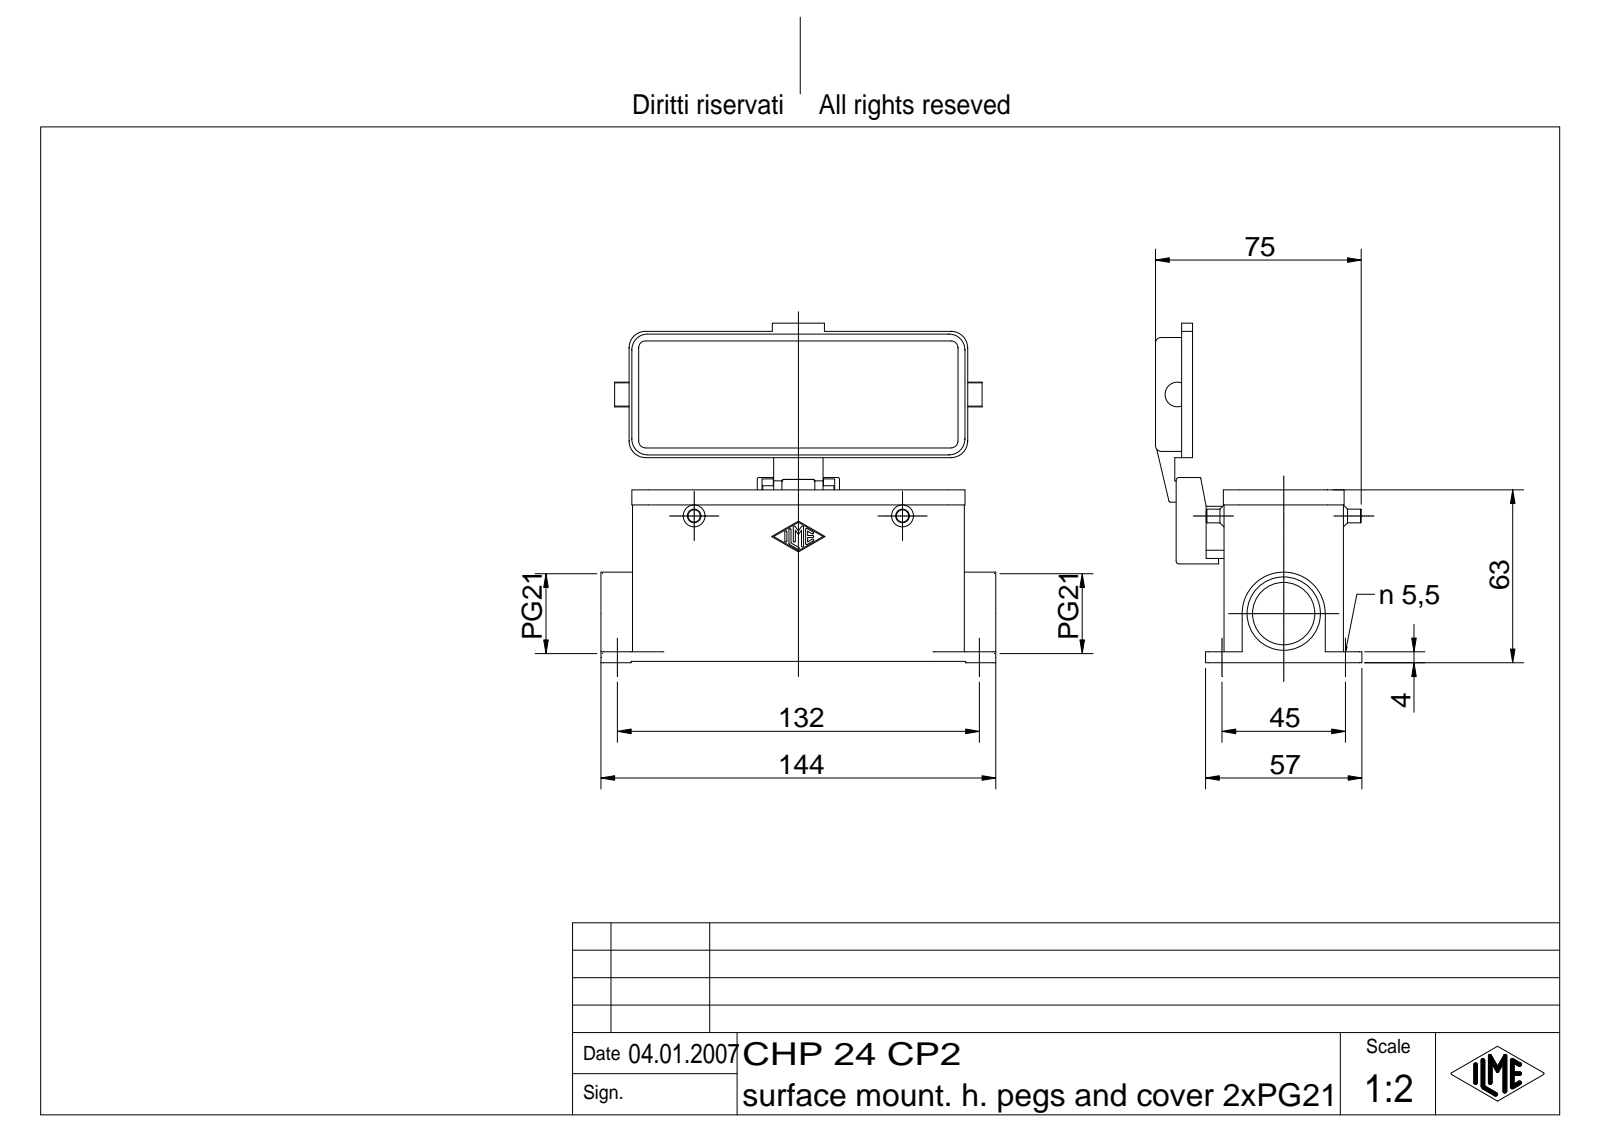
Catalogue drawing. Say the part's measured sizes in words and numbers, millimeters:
The part is named "CHP 24 CP2". Its 3-D file was written by "Autodesk Inventor 7 (AUTOMOTIVE_DESIGN)". It is 1 solid with 469 faces: 195 planar, 164 cylindrical and 110 other. Overall it measures 144 by 123.75 by 75.25 millimeters. Its volume is 126 305 cubic millimeters and its surface area 80 127 square millimeters. Round holes: 4 of diameter 5.5, 1 of diameter 4, 1 of diameter 5, 1 of diameter 22.78, 1 of diameter 26.78. Round bosses or shafts: 2 of diameter 5, 2 of diameter 3, 1 of diameter 7, 1 of diameter 4. Partial cylindrical surfaces (rounded edges, fillets, slot ends): 14 of radius 0.38, 14 of radius 1, 12 of radius 6, 10 of radius 0.5, 8 of radius 0.7, 8 of radius 2, 4 of radius 2.5, 4 of radius 3. The main face-to-face distances are 3, 40.5, 43.5, 2.5, 37.5, 63, 3.5, 22.5, 68.5, 66. The hole center spacings are 45, 132, 139.46.
